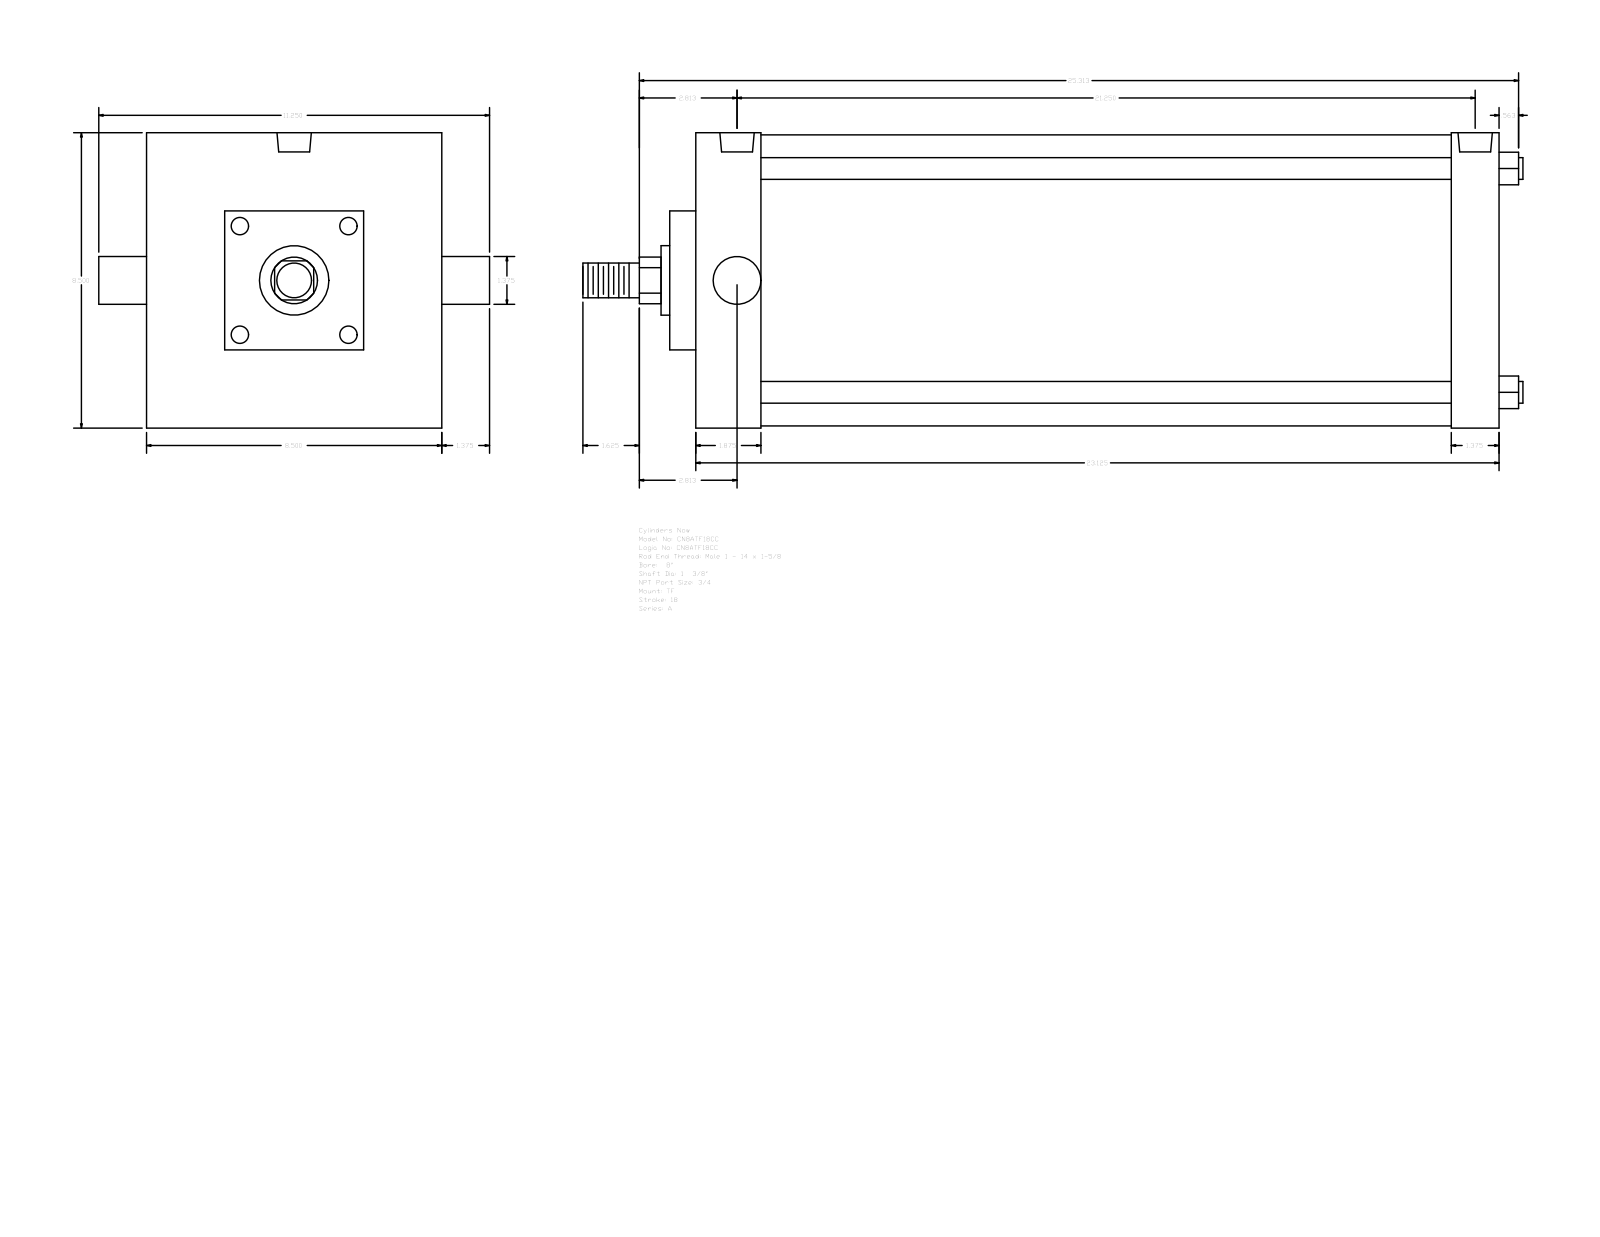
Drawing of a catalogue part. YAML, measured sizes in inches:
part_name: "A_TF__0800_1.375"
step_written_by: "GSSL Pune (CONFIG_CONTROL_DESIGN)"
units: inches
bodies: {solids: 0, faces: 89, planar: 65, cylindrical: 24, other: 0}
overall_size: [27.063, 11.25, 8.5]
round_holes:
  - {diameter: 0.594, count: 3}
  - {diameter: 0.989, count: 2}
round_bosses_or_shafts:
  - {diameter: 0.625, count: 4}
  - {diameter: 1.375, count: 2}
  - {diameter: 8.375, count: 1}
  - {diameter: 2, count: 1}
  - {diameter: 1, count: 1}
partial_cylinders:
  - {radius: 0.672, count: 1}
face_to_face_distances: [23.125, 8.5, 1.875, 21.25, 21.75, 19.875, 1.375, 0.75, 2.625, 22.5]
hole_center_spacings: [0.25, 21, 20.75, 21.25]
